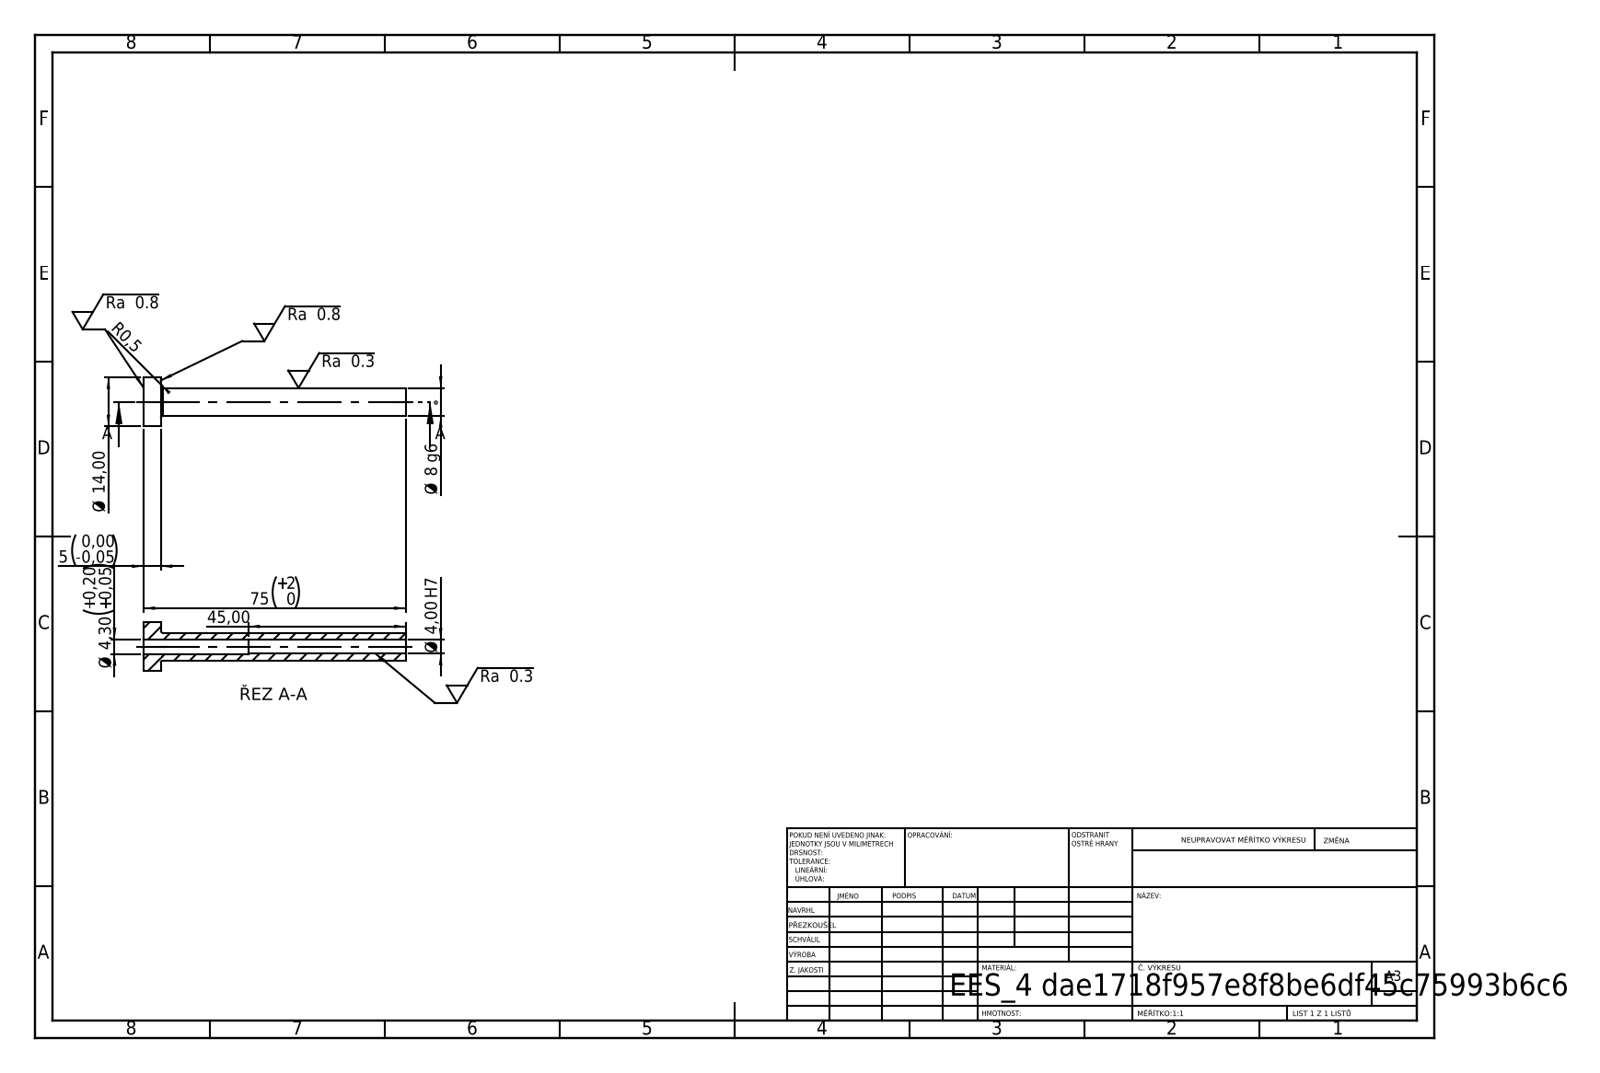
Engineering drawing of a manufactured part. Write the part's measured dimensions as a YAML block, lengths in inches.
step_written_by: "SolidWorks 2019 (CONFIG_CONTROL_DESIGN)"
units: inches
bodies: {solids: 1, faces: 14, planar: 4, cylindrical: 8, other: 2}
overall_size: [2.953, 0.551, 0.551]
volume: 0.201
surface_area: 5.002
round_holes:
  - {diameter: 0.157, count: 1}
  - {diameter: 0.169, count: 1}
round_bosses_or_shafts:
  - {diameter: 0.551, count: 1}
  - {diameter: 0.315, count: 1}
face_to_face_distances: [0.197, 2.953, 2.756, 1.181, 0.984, 1.772]
